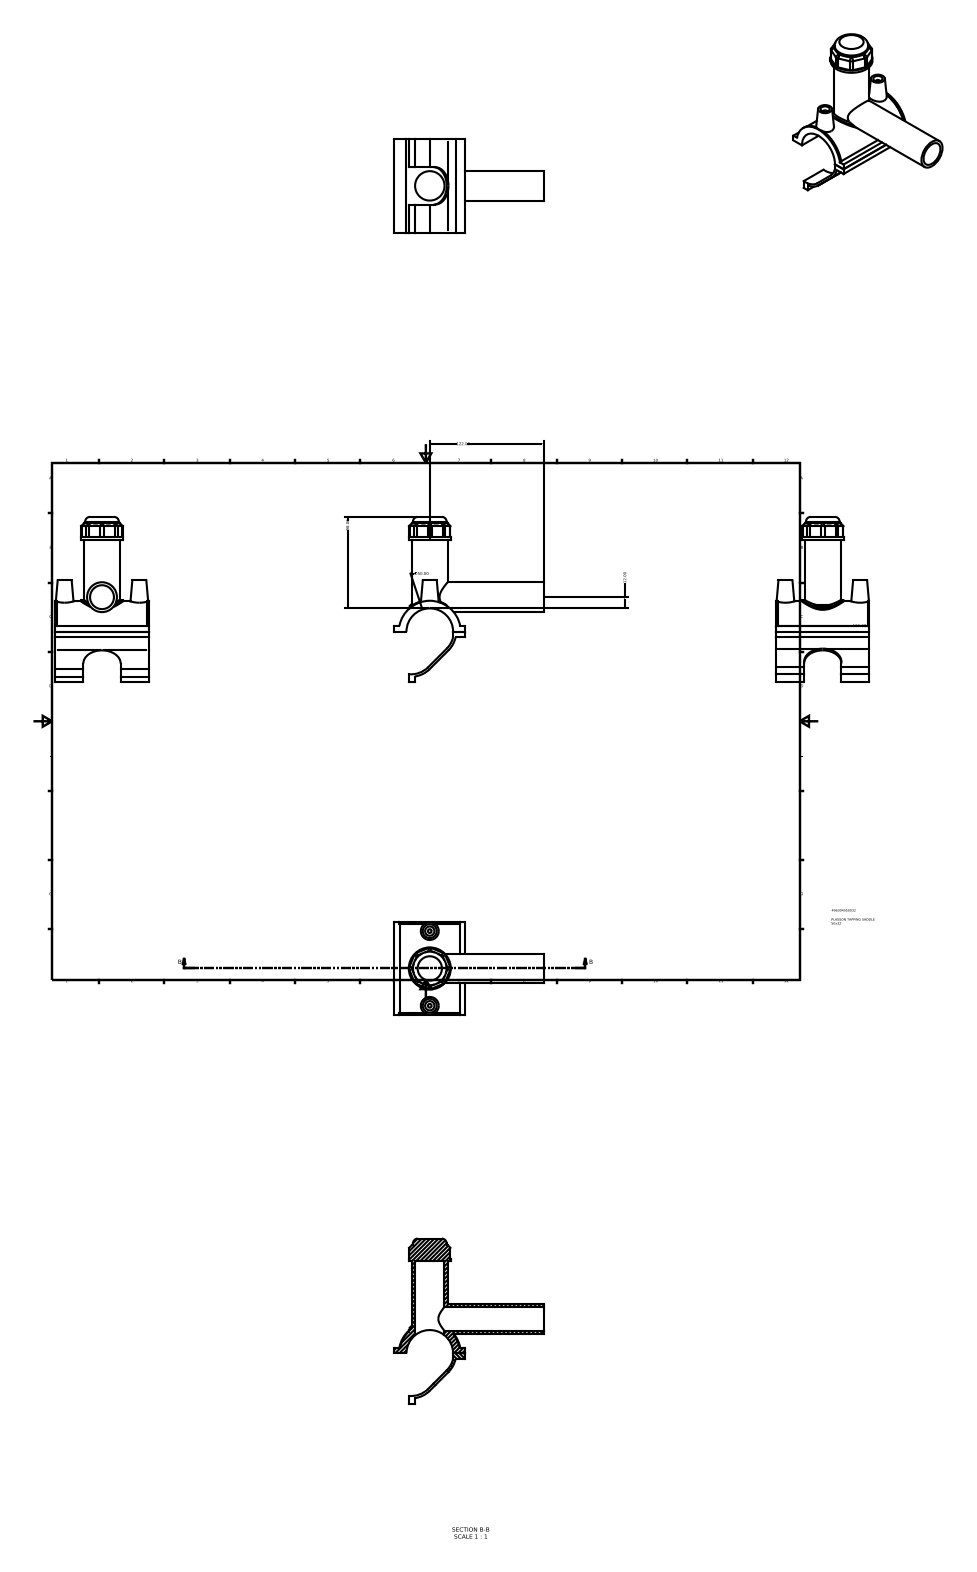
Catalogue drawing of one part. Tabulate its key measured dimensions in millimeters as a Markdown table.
| quantity | value |
| --- | --- |
| part name | 496304050032 |
| STEP written by | Autodesk Inventor 2015 (AUTOMOTIVE_DESIGN) |
| units | millimeters |
| bodies | 2 solids, 111 faces (66 planar, 32 cylindrical, 13 other) |
| overall size | 177.37 × 160 × 100 |
| volume | 185 957 mm³ |
| surface area | 79 468 mm² |
| round holes (diameter × count) | 10 × 2, 25.6 × 1, 31.5 × 1 |
| round bosses / shafts (diameter × count) | 4 × 2, 45 × 1, 38.25 × 1, 36 × 1, 32 × 1 |
| partial cylindrical surfaces (radius × count) | 5 × 8, 25.68 × 2, 28.28 × 2, 20 × 1, 21.38 × 1, 25 × 1, 32.5 × 1, 33.15 × 1 |
| main face-to-face distances | 6.2, 2.6, 98.45, 92.25, 100, 12.4, 104.65, 76, 41.58, 63 |
| hole center spacings | 40, 80 |
